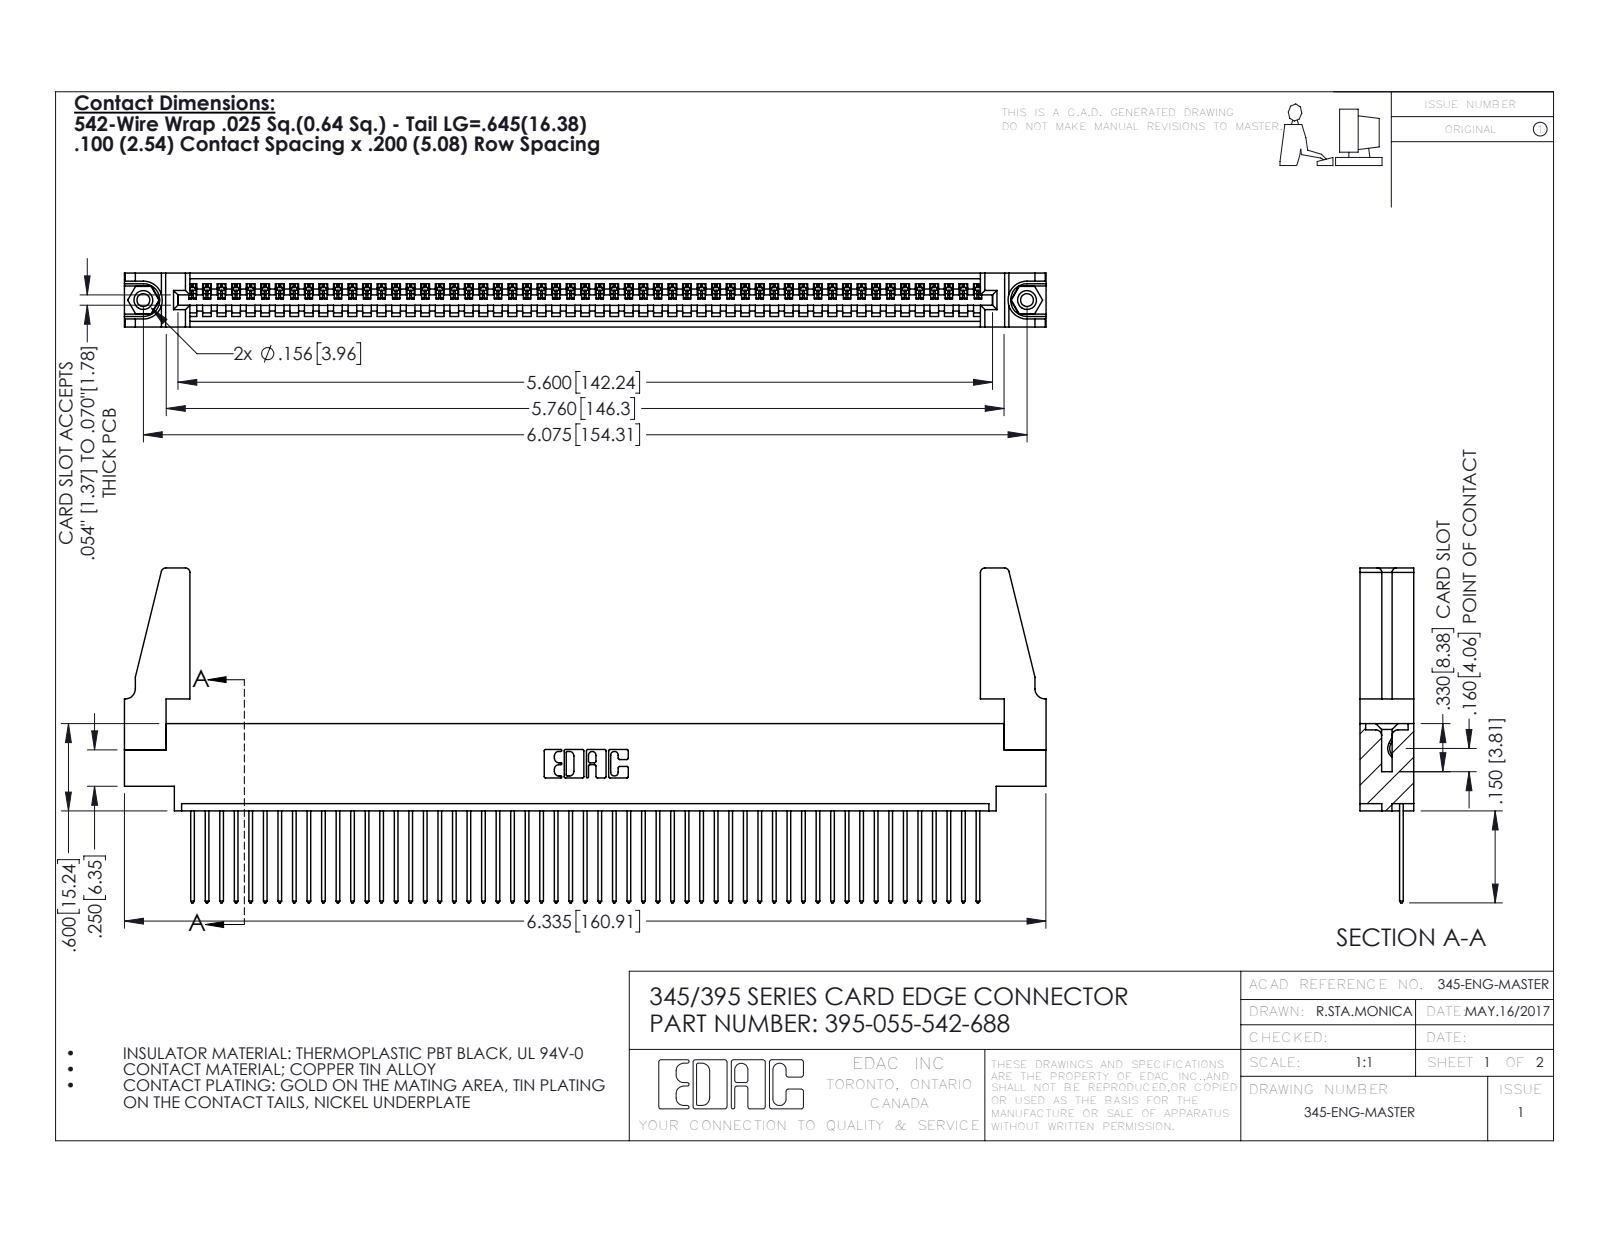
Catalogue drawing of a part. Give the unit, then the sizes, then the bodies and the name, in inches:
Units: inches
Overall size (bounding box): 6.336 × 2.302 × 0.37
Round holes (diameter × count): ⌀0.089 ×2, ⌀0.125 ×2, ⌀0.156 ×2, ⌀0.064 ×1
Round bosses / shafts (diameter × count): ⌀0.155 ×2
Partial cylindrical surfaces — rounded edges, fillets, slot ends (radius × count): R0.006 ×110, R0.01 ×110, R0.01 ×22, R0.03 ×8, R0.007 ×6, R0.031 ×6, R0.026 ×3, R0.031 ×2
Main face-to-face distances: 0.072, 0.298, 0.37, 0.098, 0.272, 0.025, 0.2, 0.225, 0.175, 0.149
Hole centre spacings: 0.27, 5.839, 6.075
Volume: 1.138 in³ · Surface area: 38.24 in²
Bodies: 60 solids, 3444 faces (2356 planar, 1072 cylindrical, 16 other)
Part name (STEP PRODUCT): 345-250-001_345-250-001-102; 345 Part_0.170 Offset - 0.156 Dia-TH; 395-055-542-688; 345-220-078_345-220-088 (+1 more)
STEP written by: SolidWorks 2016 (CONFIG_CONTROL_DESIGN)
